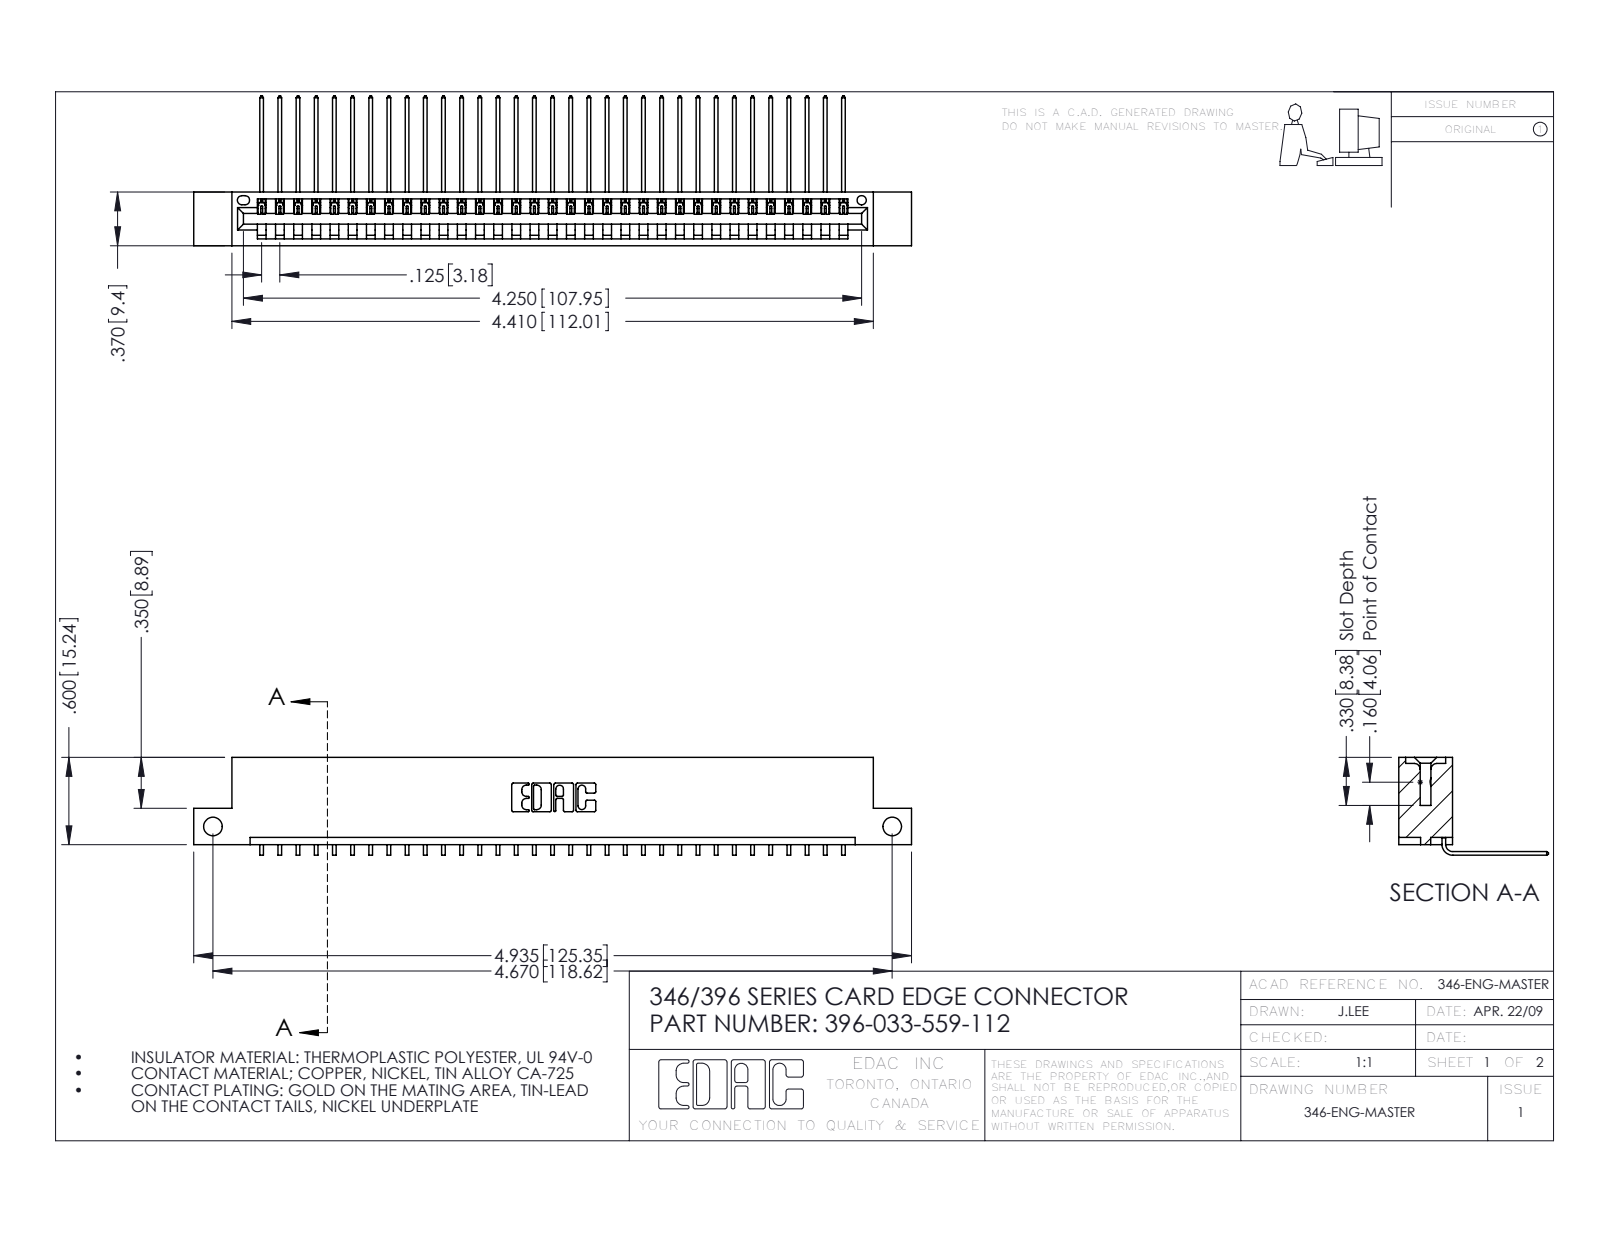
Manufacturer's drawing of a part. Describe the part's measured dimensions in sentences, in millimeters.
The part is named "345-292-001_558 559 Tail - 1; 396-033-559-112; 346 Part_Flush Mounting Lugs - Side Mount". Its 3-D file was written by "SolidWorks 2016 (CONFIG_CONTROL_DESIGN)". It is 34 solids with 2102 faces: 1462 planar, 640 cylindrical and 0 other. Overall it measures 125.3 by 26.2 by 17.1 millimeters. Its volume is 12 000 cubic millimeters and its surface area 15 360 square millimeters. Round holes: 2 of diameter 3.3, 1 of diameter 1.6. Partial cylindrical surfaces (rounded edges, fillets, slot ends): 66 of radius 0.2, 22 of radius 0.3, 6 of radius 0.2, 6 of radius 0.8, 3 of radius 0.7, 2 of radius 0.8, 2 of radius 1, 1 of radius 0.4. The main face-to-face distances are 1.2, 8.2, 9.4, 6.4, 1.8, 0.6, 7.6, 3.8, 5.6, 2.5. The hole center spacings are 118.6.
